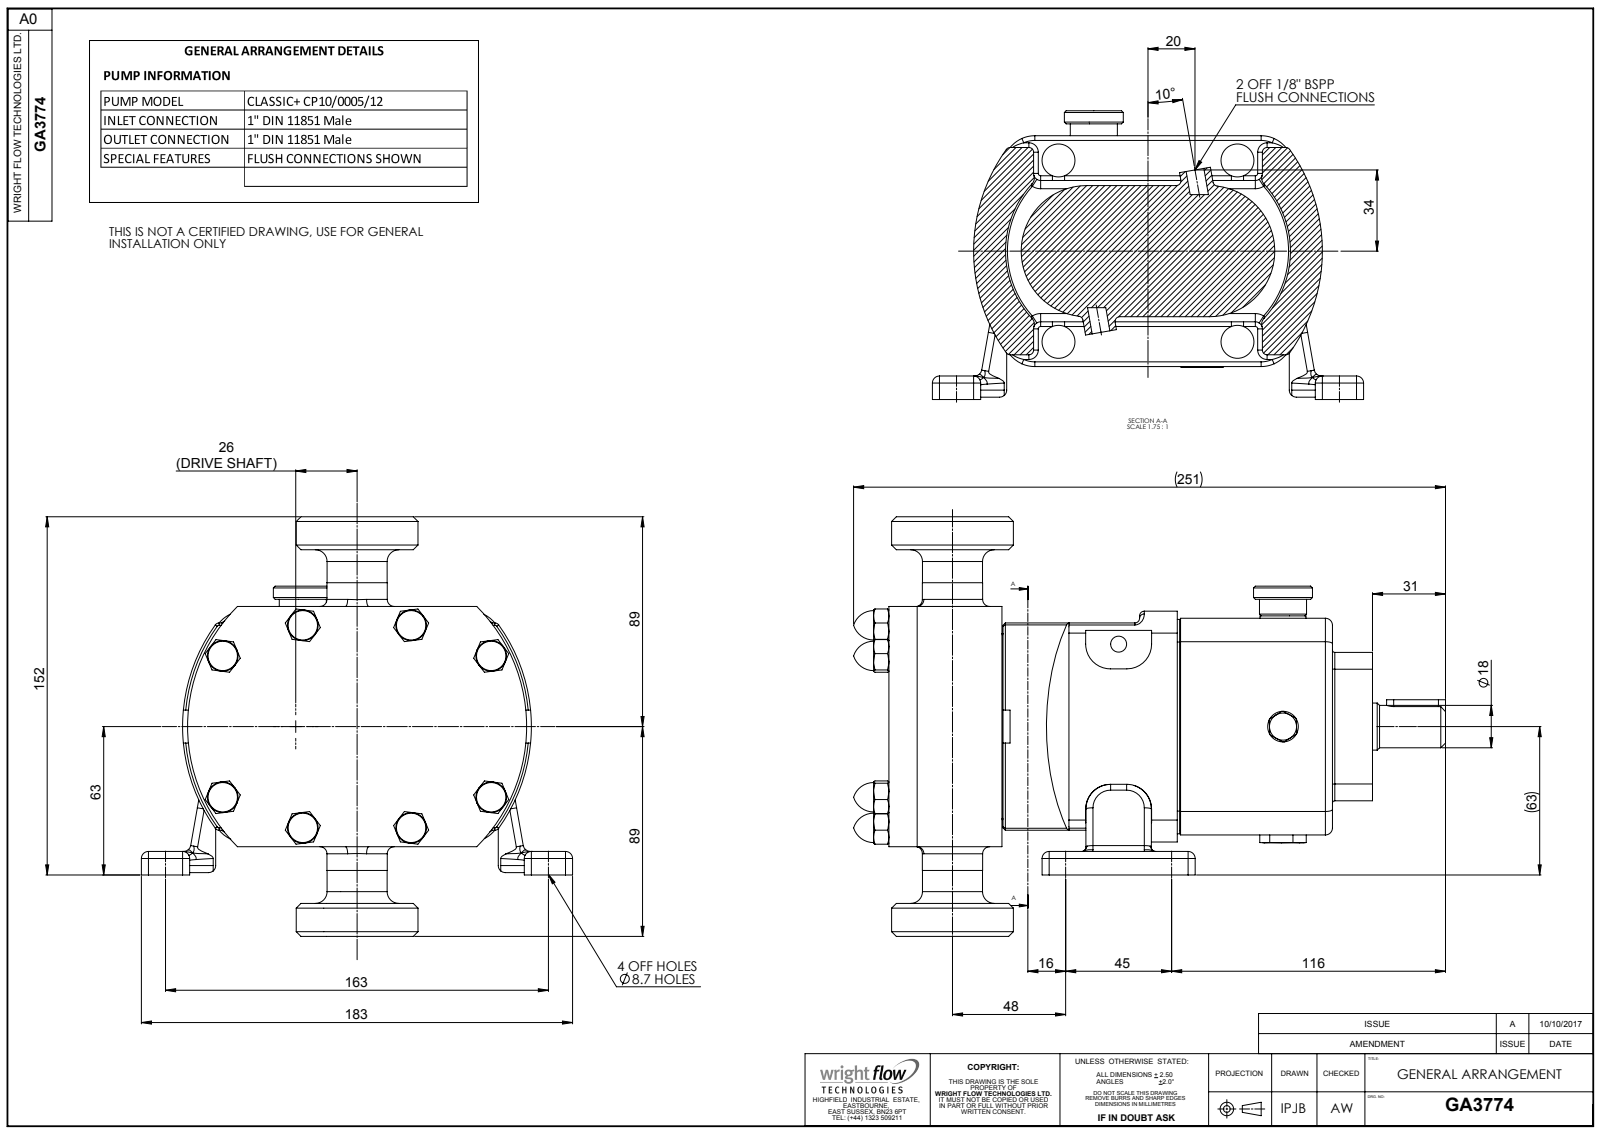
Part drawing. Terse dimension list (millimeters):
name: Copy of Z94-5031-11 - 1 INCH DIN11851^GA3774; GA3774; Copy of CP10-0005-12 V L^GA3774
written by: SolidWorks 2023 (AUTOMOTIVE_DESIGN)
unit: mm
bodies: 3 solids, 789 faces (252 planar, 228 cylindrical, 309 other)
size: 251.35 × 183.1 × 178.15
volume: 2 273 000 mm³; area: 181 278 mm²
holes: 4× ⌀8.5, 4× ⌀14, 2× ⌀7.63, 1× ⌀6.8, 1× ⌀22.2, 1× ⌀22.53, 1× ⌀26, 1× ⌀39.8
bosses: 3× ⌀30, 1× ⌀51.7, 1× ⌀25.6, 1× ⌀25.5, 1× ⌀25.02, 1× ⌀19.99, 1× ⌀19.98, 1× ⌀19.5
rounds: 32× R2, 32× R3, 12× R13.5, 6× R3.5, 6× R10.5, 4× R5.5, 4× R6, 4× R9
face distances: 205.35, 102, 92, 124, 81.35, 14, 2, 97.01, 5.01, 4.99
hole spacings: 45, 76, 77.02, 108.2, 162.6, 168.71, 51.23, 75.07
